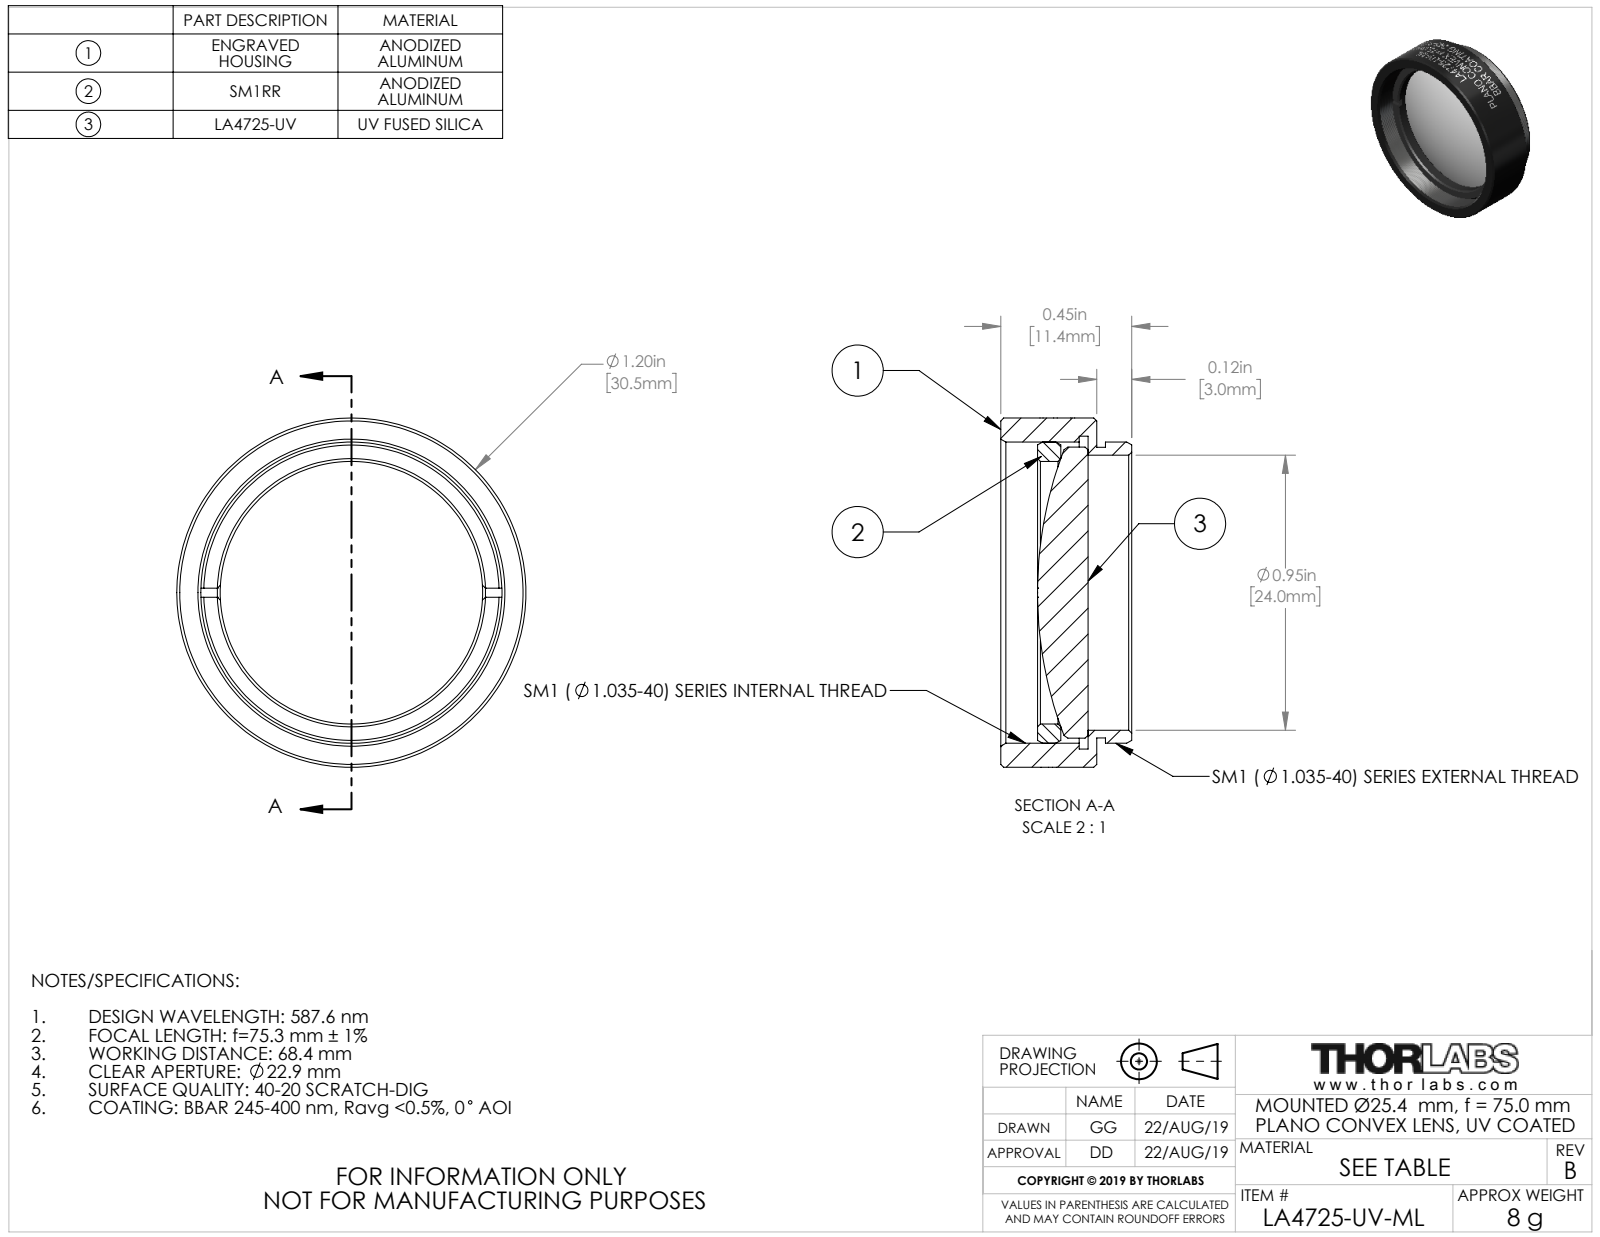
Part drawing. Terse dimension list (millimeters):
name: 24455-E0W
written by: SolidWorks 2018 (CONFIG_CONTROL_DESIGN)
unit: mm
bodies: 3 solids, 154 faces (20 planar, 106 cylindrical, 28 other)
size: 30.48 × 30.48 × 11.43
volume: 3 707 mm³; area: 4 312 mm²
holes: 1× ⌀22.91, 1× ⌀24, 1× ⌀26.29, 1× ⌀27.3
bosses: 1× ⌀30.48, 1× ⌀26.29, 1× ⌀25.4, 1× ⌀25.37
face distances: 0.76, 8.38, 7.62, 3.13, 2.37, 5.25, 5.16, 4.4, 2.03, 3.22
